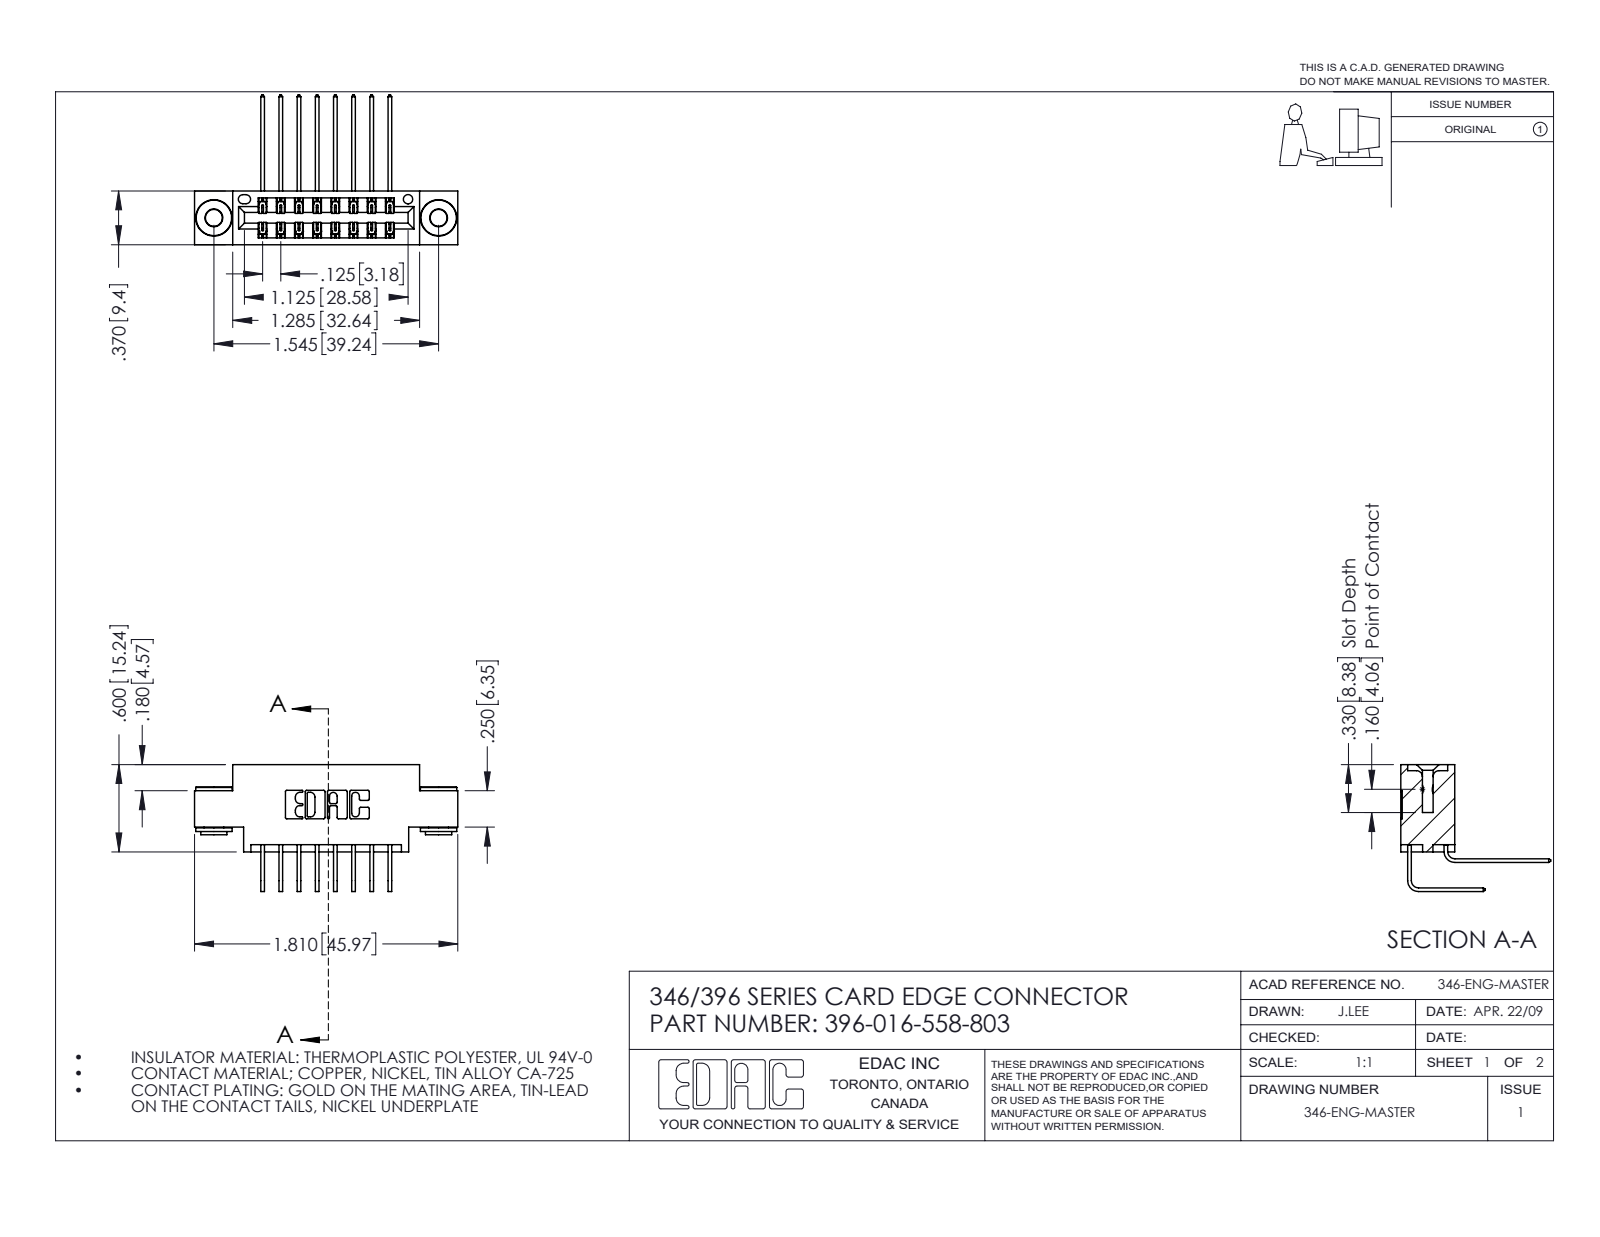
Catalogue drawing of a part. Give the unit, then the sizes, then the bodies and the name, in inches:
Units: inches
Overall size (bounding box): 1.81 × 1.03 × 0.873
Round holes (diameter × count): ⌀0.116 ×2, ⌀0.156 ×2, ⌀0.064 ×1
Round bosses / shafts (diameter × count): ⌀0.25 ×2, ⌀0.18 ×2, ⌀0.136 ×2
Partial cylindrical surfaces — rounded edges, fillets, slot ends (radius × count): R0.006 ×24, R0.01 ×22, R0.007 ×6, R0.031 ×6, R0.026 ×3, R0.014 ×2, R0.022 ×2, R0.024 ×2
Main face-to-face distances: 0.25, 0.37, 0.048, 0.322, 0.025, 0.072, 0.298, 0.275, 0.148, 0.222
Hole centre spacings: 0.246, 1.341, 1.545
Volume: 0.255 in³ · Surface area: 9.366 in²
Bodies: 19 solids, 1028 faces (682 planar, 338 cylindrical, 8 other)
Part name (STEP PRODUCT): 345-292-001_558 559 Tail - 1; 345-250-002_345-250-002-102; 346 Part_0.170 Offset - 0.156 Dia-TH; 396-016-558-803 (+1 more)
STEP written by: SolidWorks 2016 (CONFIG_CONTROL_DESIGN)
